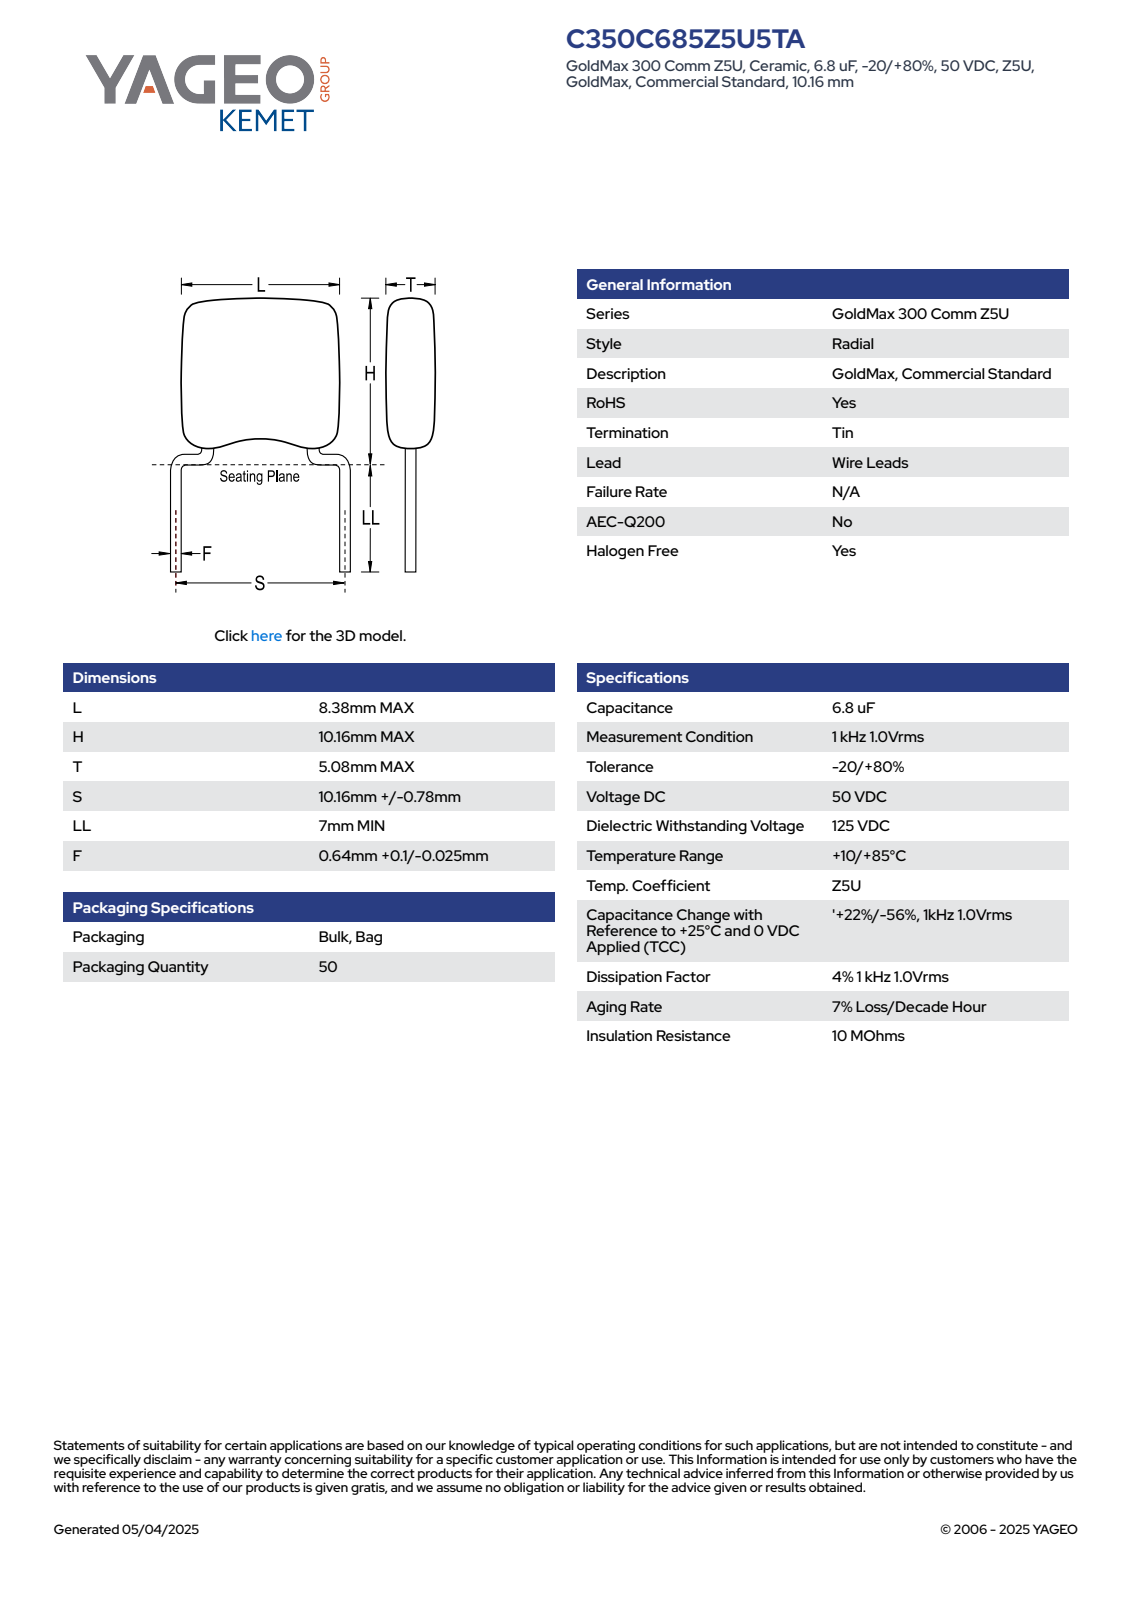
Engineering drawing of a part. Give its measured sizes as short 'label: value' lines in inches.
name: CCR_SB_8.38X10.16_L8.38H10.16T5.08S10.16LL7F0.64
written by: SolidWorks 2014 (AUTOMOTIVE_DESIGN)
unit: in
bodies: 4 solids, 99 faces (67 planar, 14 cylindrical, 18 other)
size: 0.676 × 0.425 × 0.2
volume: 0.02 in³; area: 0.477 in²
bosses: 2× ⌀0.025
rounds: 10× R0.039
face distances: 0.2, 0.33, 0.313, 0.171, 0.141, 0.143, 0.028, 0.169, 0.028, 0.012
